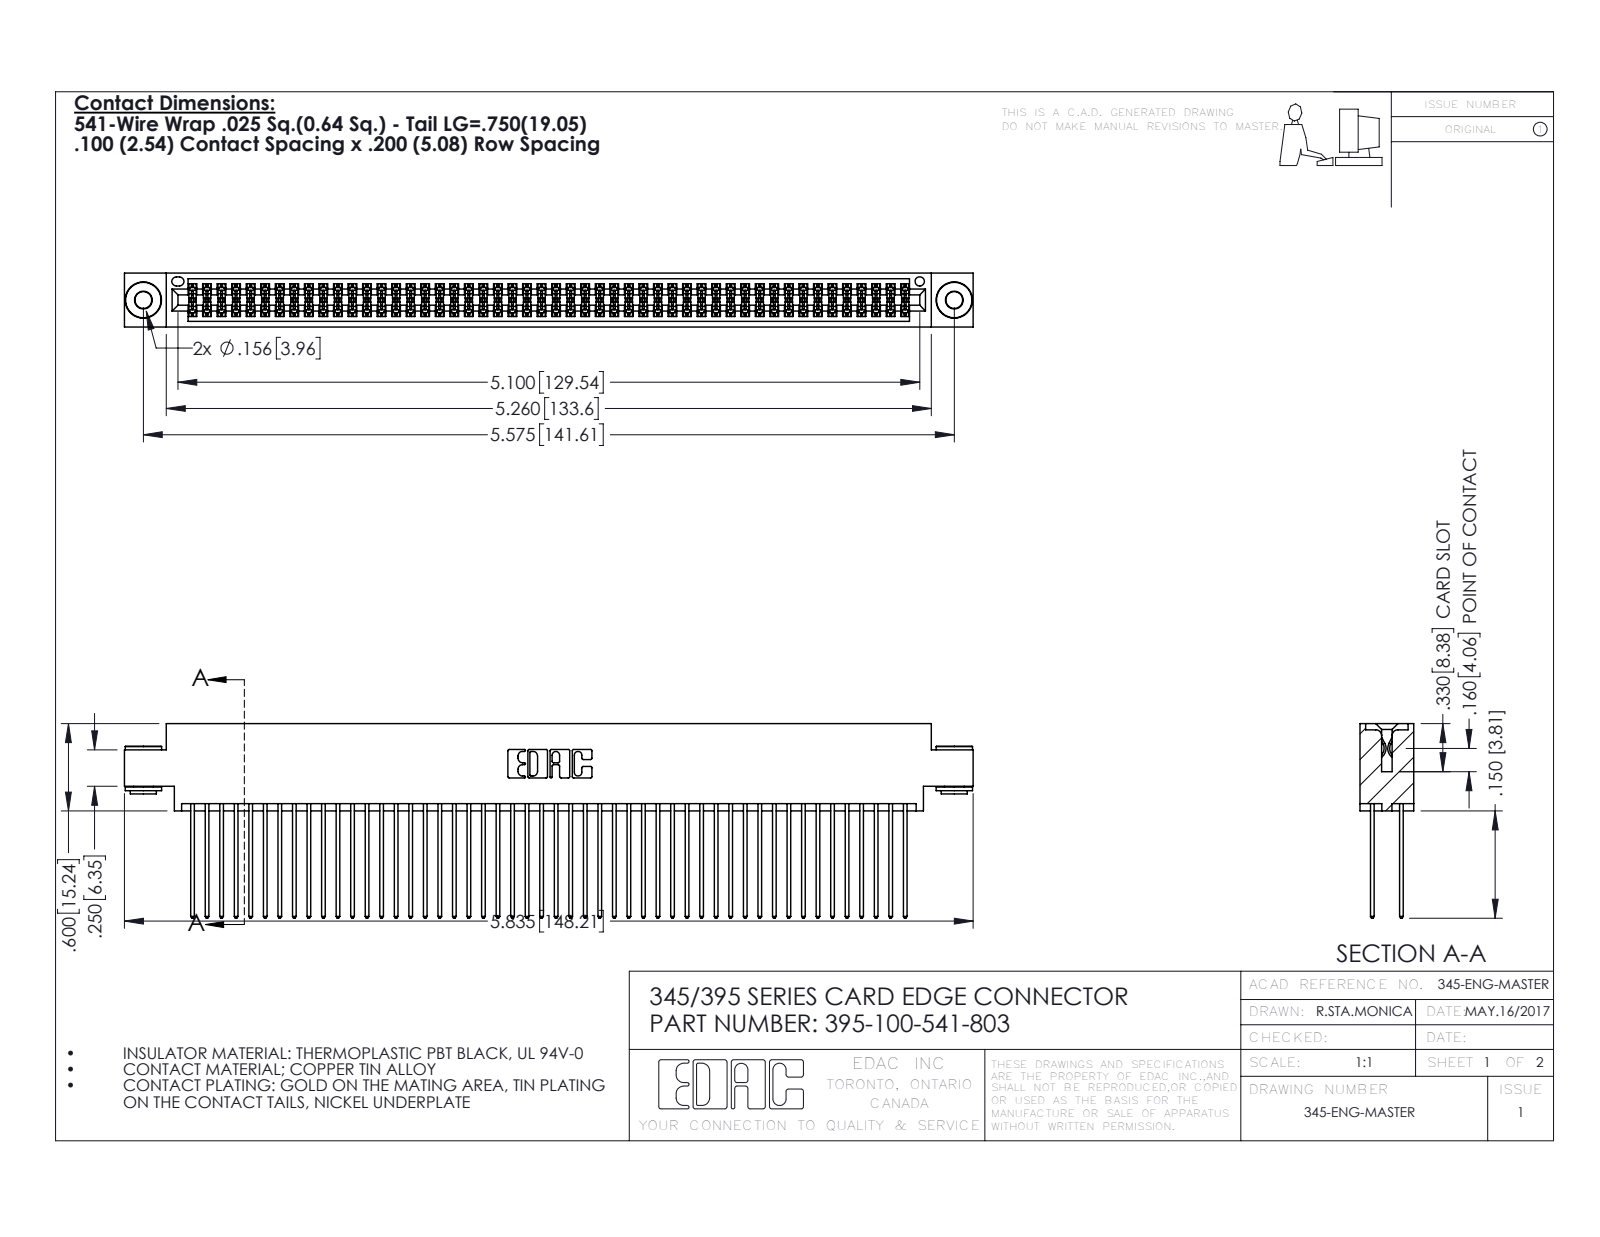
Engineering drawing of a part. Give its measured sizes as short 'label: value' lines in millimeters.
name: 345 Part_0.170 Offset - 0.156 Dia-TH; 345-250-002_345-250-002-102; 395-100-541-803; 345-292-001_345-293-141
written by: SolidWorks 2016 (CONFIG_CONTROL_DESIGN)
unit: mm
bodies: 103 solids, 5168 faces (3394 planar, 1766 cylindrical, 8 other)
size: 148.2 × 34 × 9.4
volume: 14 900 mm³; area: 25 300 mm²
holes: 2× ⌀2.9, 2× ⌀4, 1× ⌀1.6
bosses: 2× ⌀6.4, 2× ⌀4.6, 2× ⌀3.5
rounds: 150× R0.2, 100× R0.3, 22× R0.3, 6× R0.2, 6× R0.8, 3× R0.7, 2× R0.4, 2× R0.5
face distances: 1.8, 7.6, 5.1, 2.5, 6.9, 0.6, 9.4, 5.7, 4.4, 3.8
hole spacings: 6.9, 135.6, 141.6
